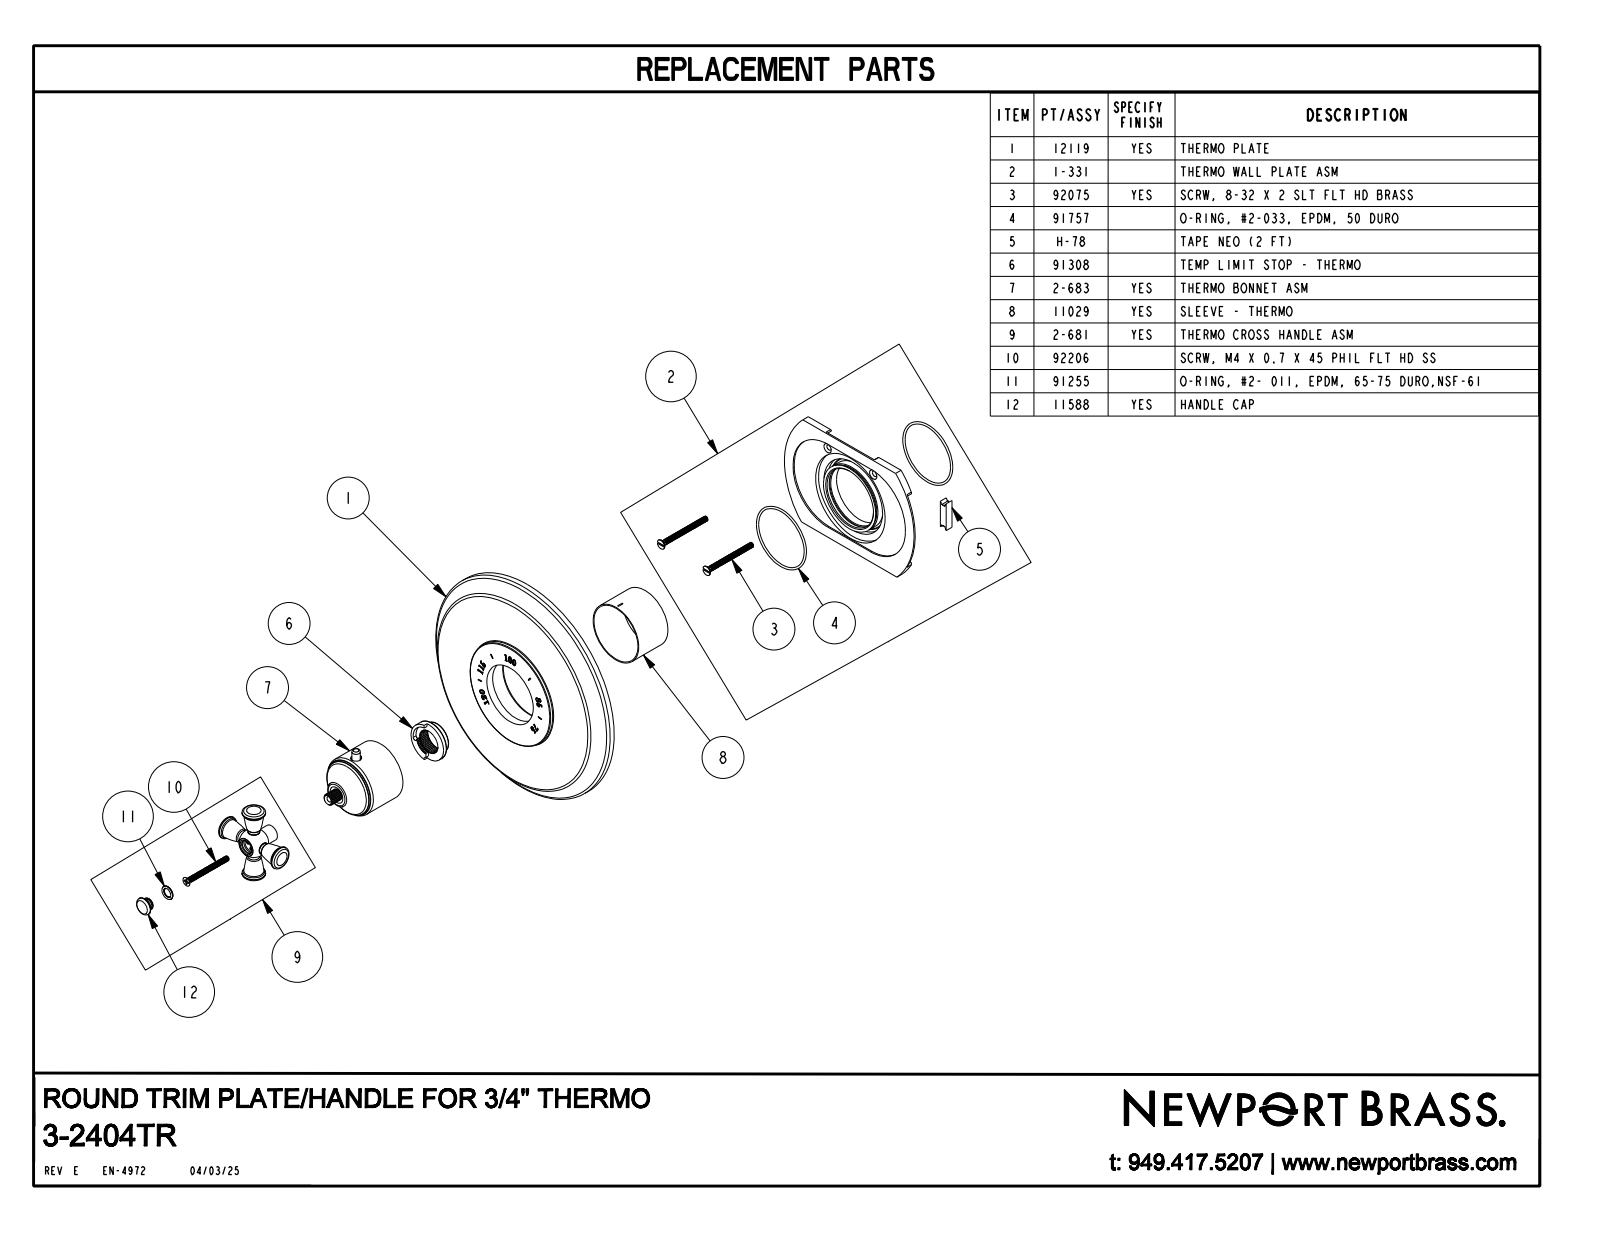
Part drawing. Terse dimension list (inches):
name: 3-2404TR
written by: CREO PARAMETRIC BY PTC INC, 2018400 (CONFIG_CONTROL_DESIGN)
unit: in
bodies: 1 solid, 138 faces (8 planar, 26 cylindrical, 104 other)
size: 7.5 × 7.5 × 3.976
volume: 32.31 in³; area: 118.2 in²
bosses: 2× ⌀0.72, 2× ⌀0.36, 1× ⌀7.5, 1× ⌀1.94, 1× ⌀0.56, 1× ⌀0.517, 1× ⌀0.26
face distances: 0.625, 0.75, 0.125, 2.836, 2.211, 2.086, 3.836, 3.211, 3.086, 1
